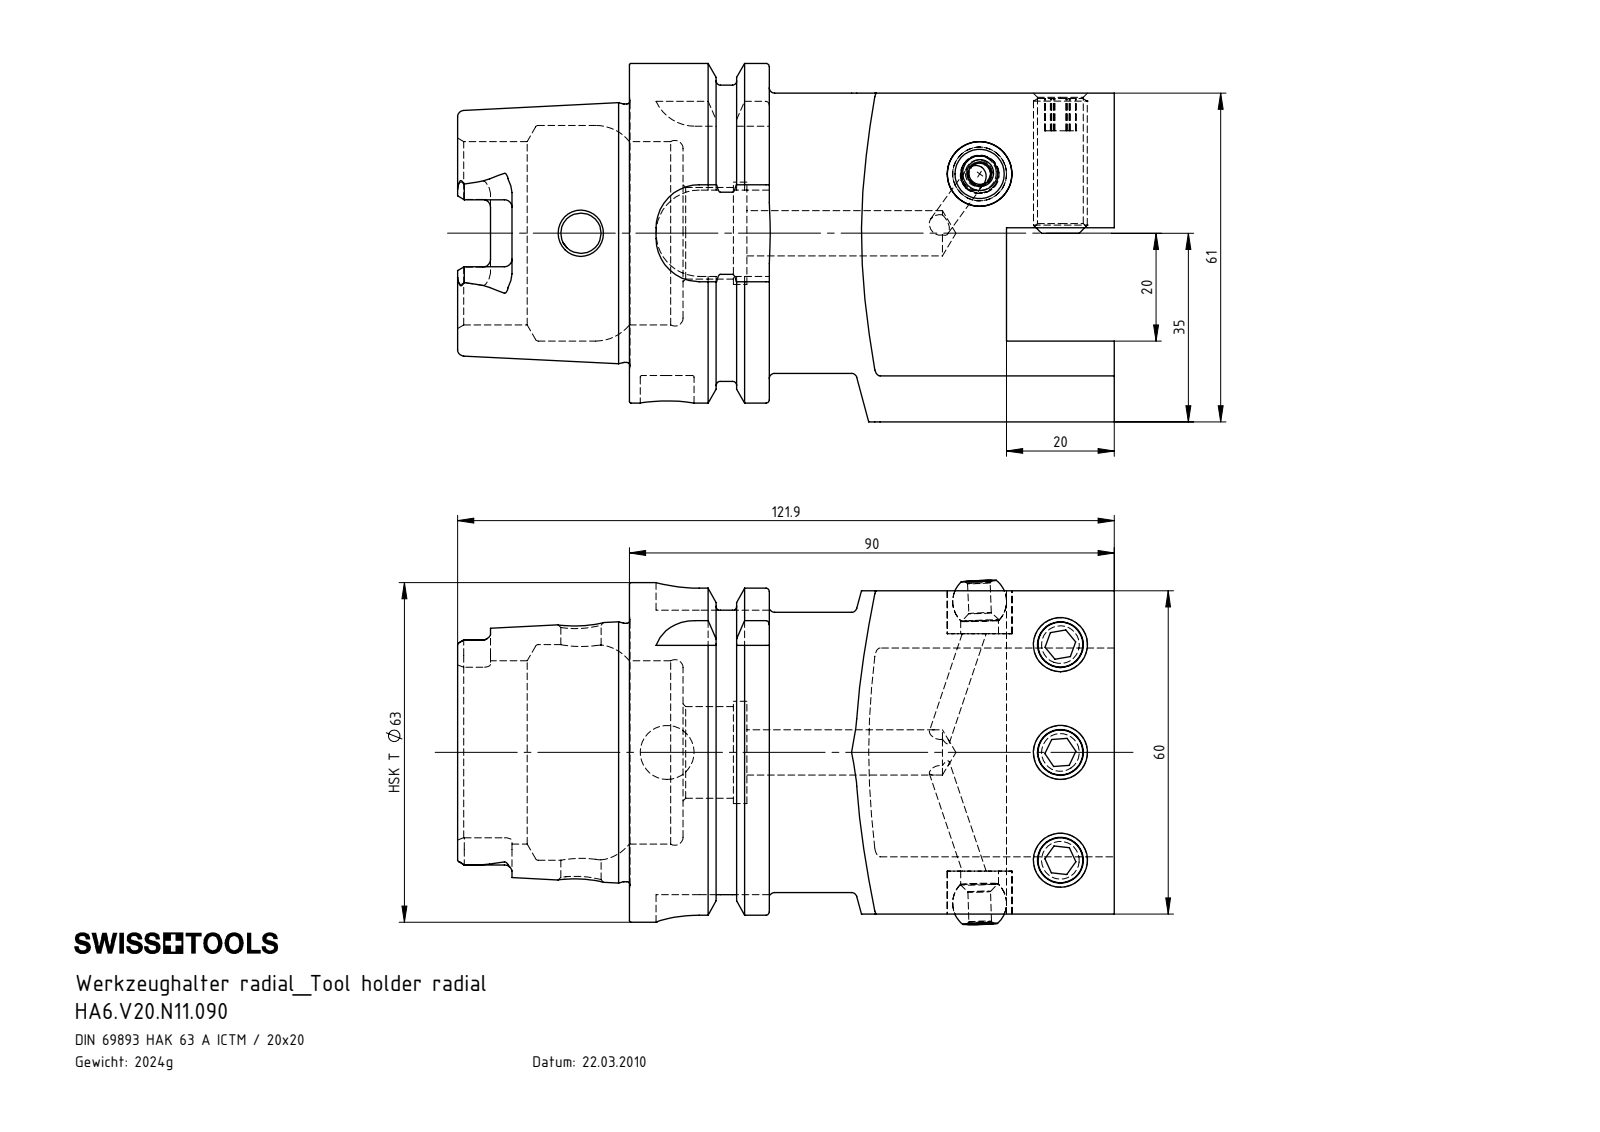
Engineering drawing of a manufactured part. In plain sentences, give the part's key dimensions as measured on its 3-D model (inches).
The part is named "KU1-U12.001.010; HA6.V20.N11.090; HA6-V20.N11.090_B; ISO 4026 - M10 x 25 (+2 more)". Its 3-D file was written by "SolidWorks 2017 (AUTOMOTIVE_DESIGN)". It is 8 solids with 273 faces: 86 planar, 79 cylindrical and 108 other. Overall it measures 4.799 by 2.618 by 2.504 inches. Its volume is 15.77 cubic inches and its surface area 75.27 square inches. Round holes: 3 of diameter 0.165, 3 of diameter 0.335, 1 of diameter 0.276, 1 of diameter 0.295, 1 of diameter 0.331, 1 of diameter 0.394, 1 of diameter 0.472, 1 of diameter 0.669, 1 of diameter 0.748, 1 of diameter 1.339, 1 of diameter 1.575. Round bosses or shafts: 3 of diameter 0.394, 1 of diameter 2.48, 1 of diameter 2.163, 1 of diameter 2.047, 1 of diameter 1.887. Partial cylindrical surfaces (rounded edges, fillets, slot ends): 6 of radius 0.055, 4 of radius 0.113, 4 of radius 0.315, 1 of radius 1.575. The main face-to-face distances are 2.362, 2.402, 0.787, 0.591, 1.811, 0.984, 2.756, 3.543, 0.827, 1.417. The hole center spacings are 0.787, 2.98, 1.575, 2.874, 2.945.
